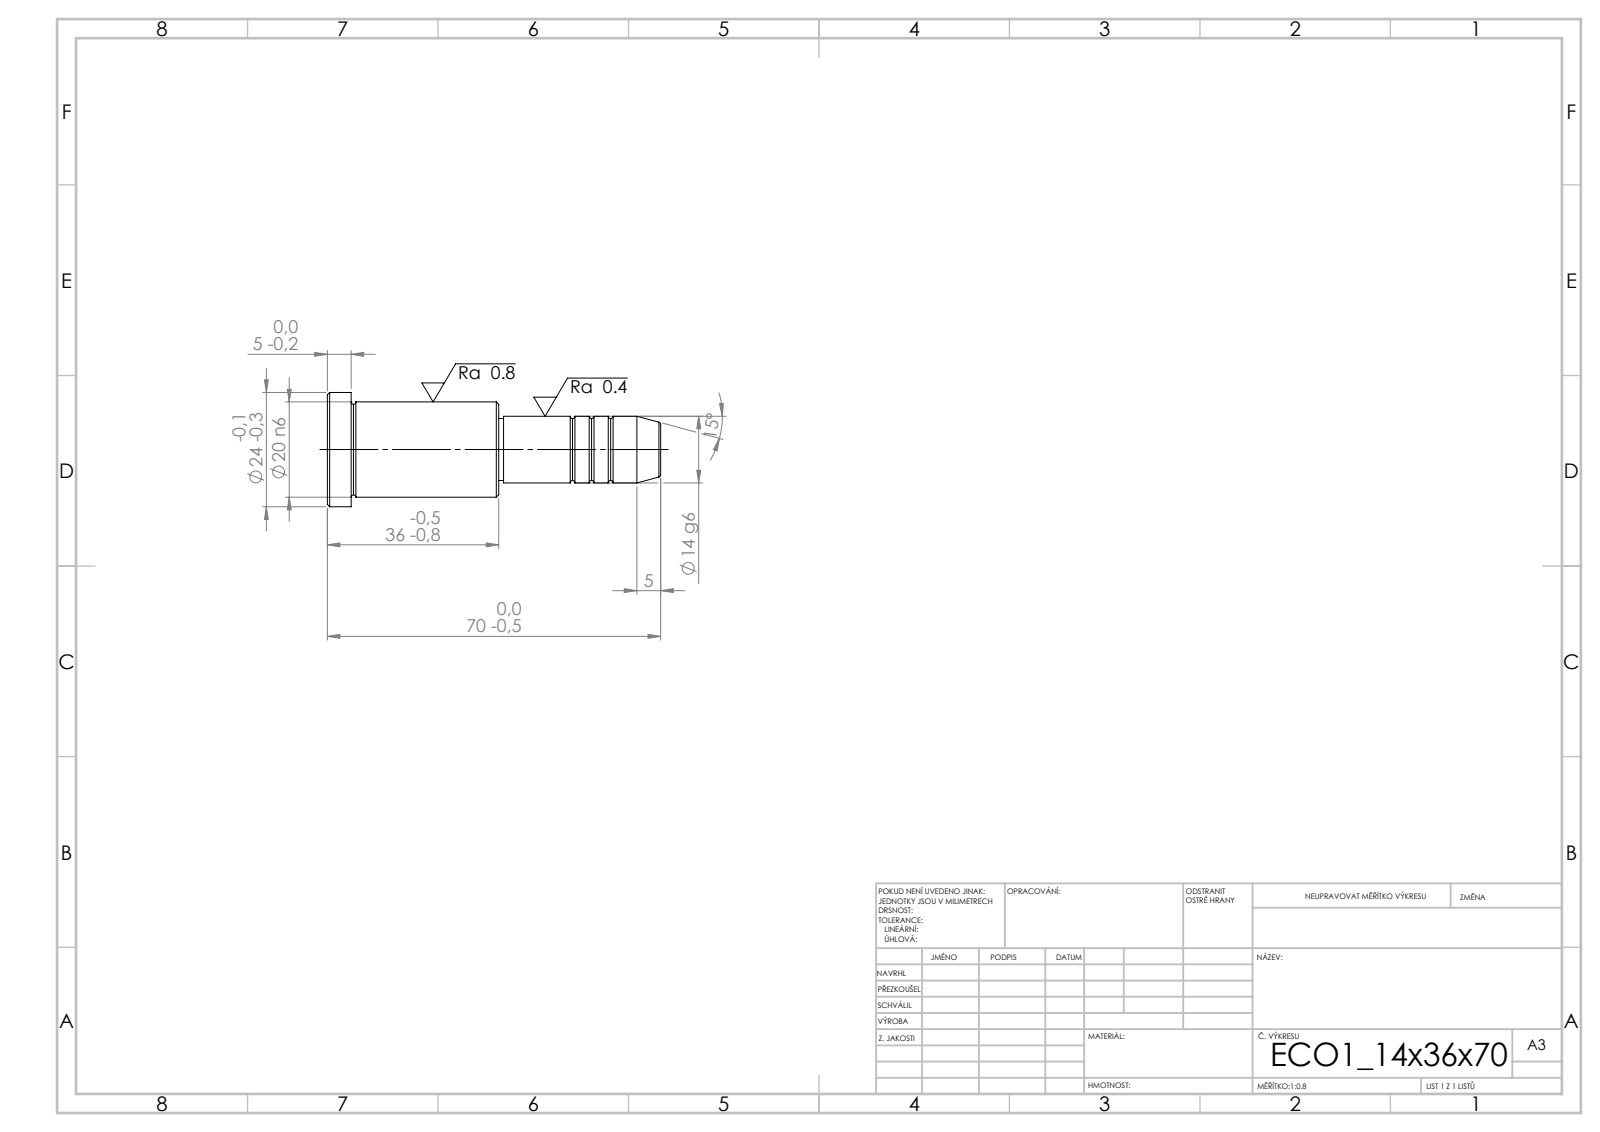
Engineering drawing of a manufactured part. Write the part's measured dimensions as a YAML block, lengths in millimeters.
step_written_by: "SolidWorks 2019 (CONFIG_CONTROL_DESIGN)"
units: millimeters
bodies: {solids: 1, faces: 43, planar: 5, cylindrical: 14, other: 24}
overall_size: [70, 24, 24]
volume: 16983
surface_area: 4750
round_bosses_or_shafts:
  - {diameter: 24, count: 1}
  - {diameter: 20, count: 1}
  - {diameter: 14, count: 1}
  - {diameter: 13, count: 1}
face_to_face_distances: [36, 31, 5, 34, 65, 70, 33, 1, 32, 37]
